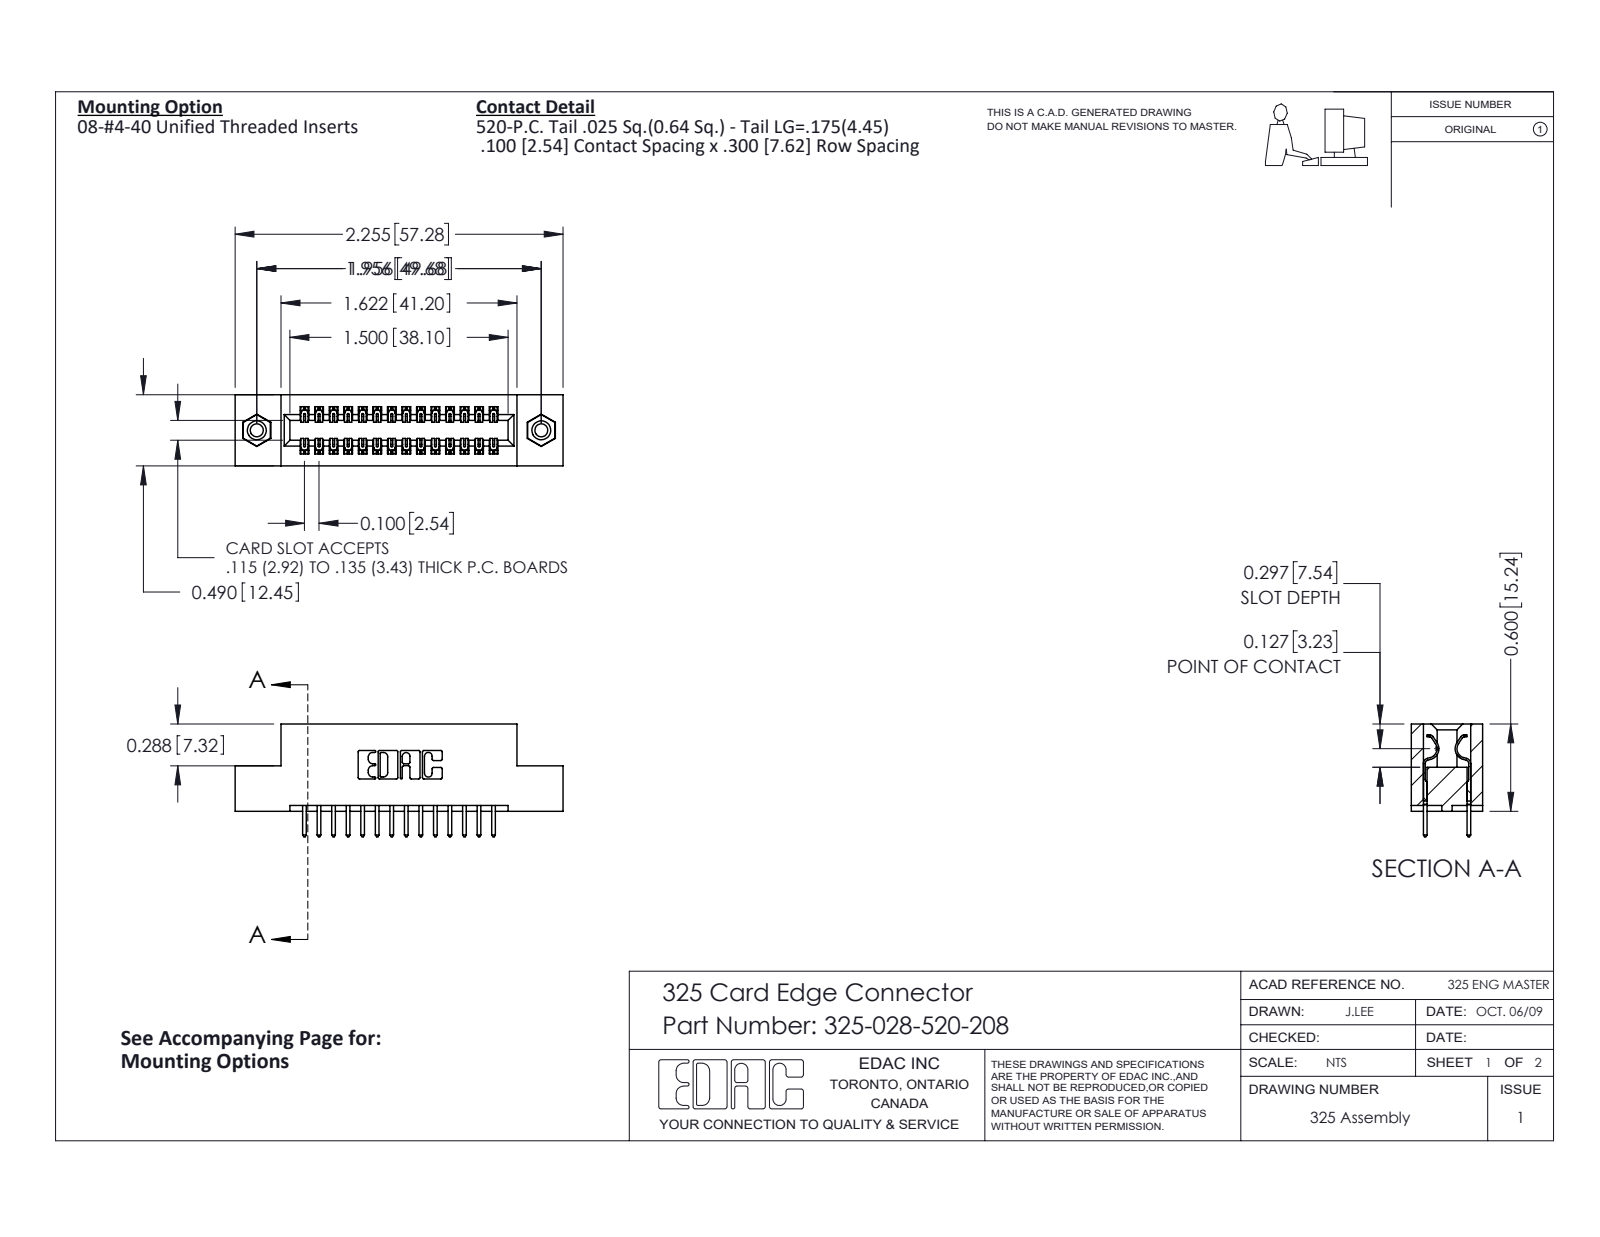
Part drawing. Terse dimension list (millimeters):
name: 325-292-001_325-293-120; 345-250-001_345-250-003-102; 325 Part_TI; 325-028-520-208
written by: SolidWorks 2016 (CONFIG_CONTROL_DESIGN)
unit: mm
bodies: 31 solids, 1630 faces (1110 planar, 504 cylindrical, 16 other)
size: 57.3 × 19.7 × 12.4
volume: 7 130 mm³; area: 7 923 mm²
holes: 2× ⌀2.3, 2× ⌀3.2, 2× ⌀4.1
bosses: 2× ⌀3.9
rounds: 42× R0.2, 28× R0.3, 22× R0.3, 6× R0.2, 6× R0.8, 3× R0.7, 2× R0.4, 2× R0.6
face distances: 2.1, 10.3, 7.6, 12.4, 2.7, 9.7, 0.6, 1, 8.3, 2.5
hole spacings: 49.7
